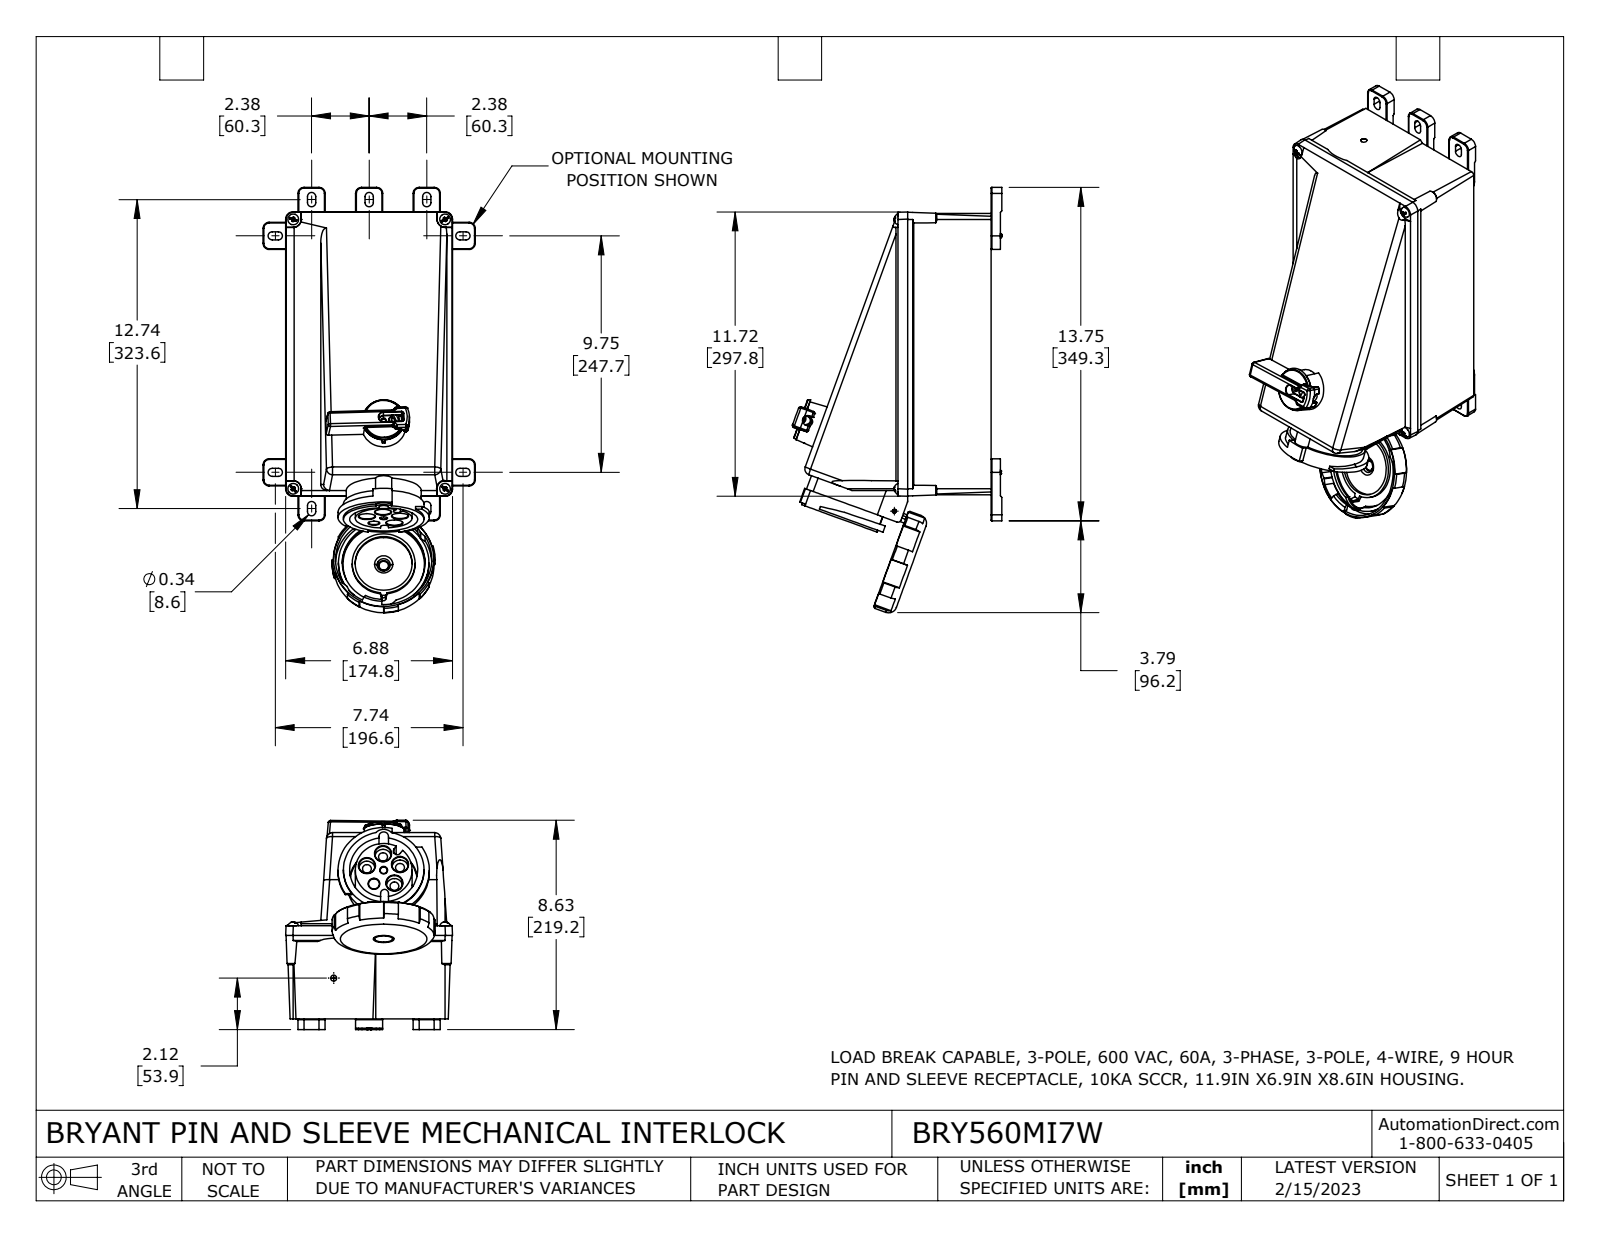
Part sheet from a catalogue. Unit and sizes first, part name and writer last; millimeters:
Units: millimetres
Overall size (bounding box): 445.6 × 219.3 × 174.8
Round holes (diameter × count): ⌀6.4 ×8, ⌀6.4 ×5, ⌀7.1 ×5, ⌀2 ×4, ⌀9.3 ×4, ⌀16.9 ×4, ⌀3 ×3, ⌀2.4 ×2, ⌀3.3 ×1, ⌀4 ×1, ⌀4.3 ×1, ⌀4.8 ×1
Round bosses / shafts (diameter × count): ⌀6.7 ×2, ⌀94.7 ×1, ⌀84.4 ×1, ⌀78.5 ×1, ⌀65.8 ×1, ⌀59.5 ×1, ⌀20.3 ×1, ⌀18.3 ×1
Partial cylindrical surfaces — rounded edges, fillets, slot ends (radius × count): R0.4 ×135, R0.8 ×53, R2 ×30, R2.3 ×24, R6.4 ×16, R1.9 ×12, R4.3 ×10, R7.4 ×5
Main face-to-face distances: 87.4, 3.6, 294.5, 136.5, 4.2, 140.1, 0.6, 3.8, 173.2, 135.9
Hole centre spacings: 17.8, 21.4, 34.7, 60.3, 18.2, 25.8, 140.9, 265.6
Volume: 6 933 000 mm³ · Surface area: 546 100 mm²
Bodies: 22 solids, 1825 faces (730 planar, 642 cylindrical, 453 other)
Part name (STEP PRODUCT): BRY560MI7W
STEP written by: SolidWorks 2021 (CONFIG_CONTROL_DESIGN)
